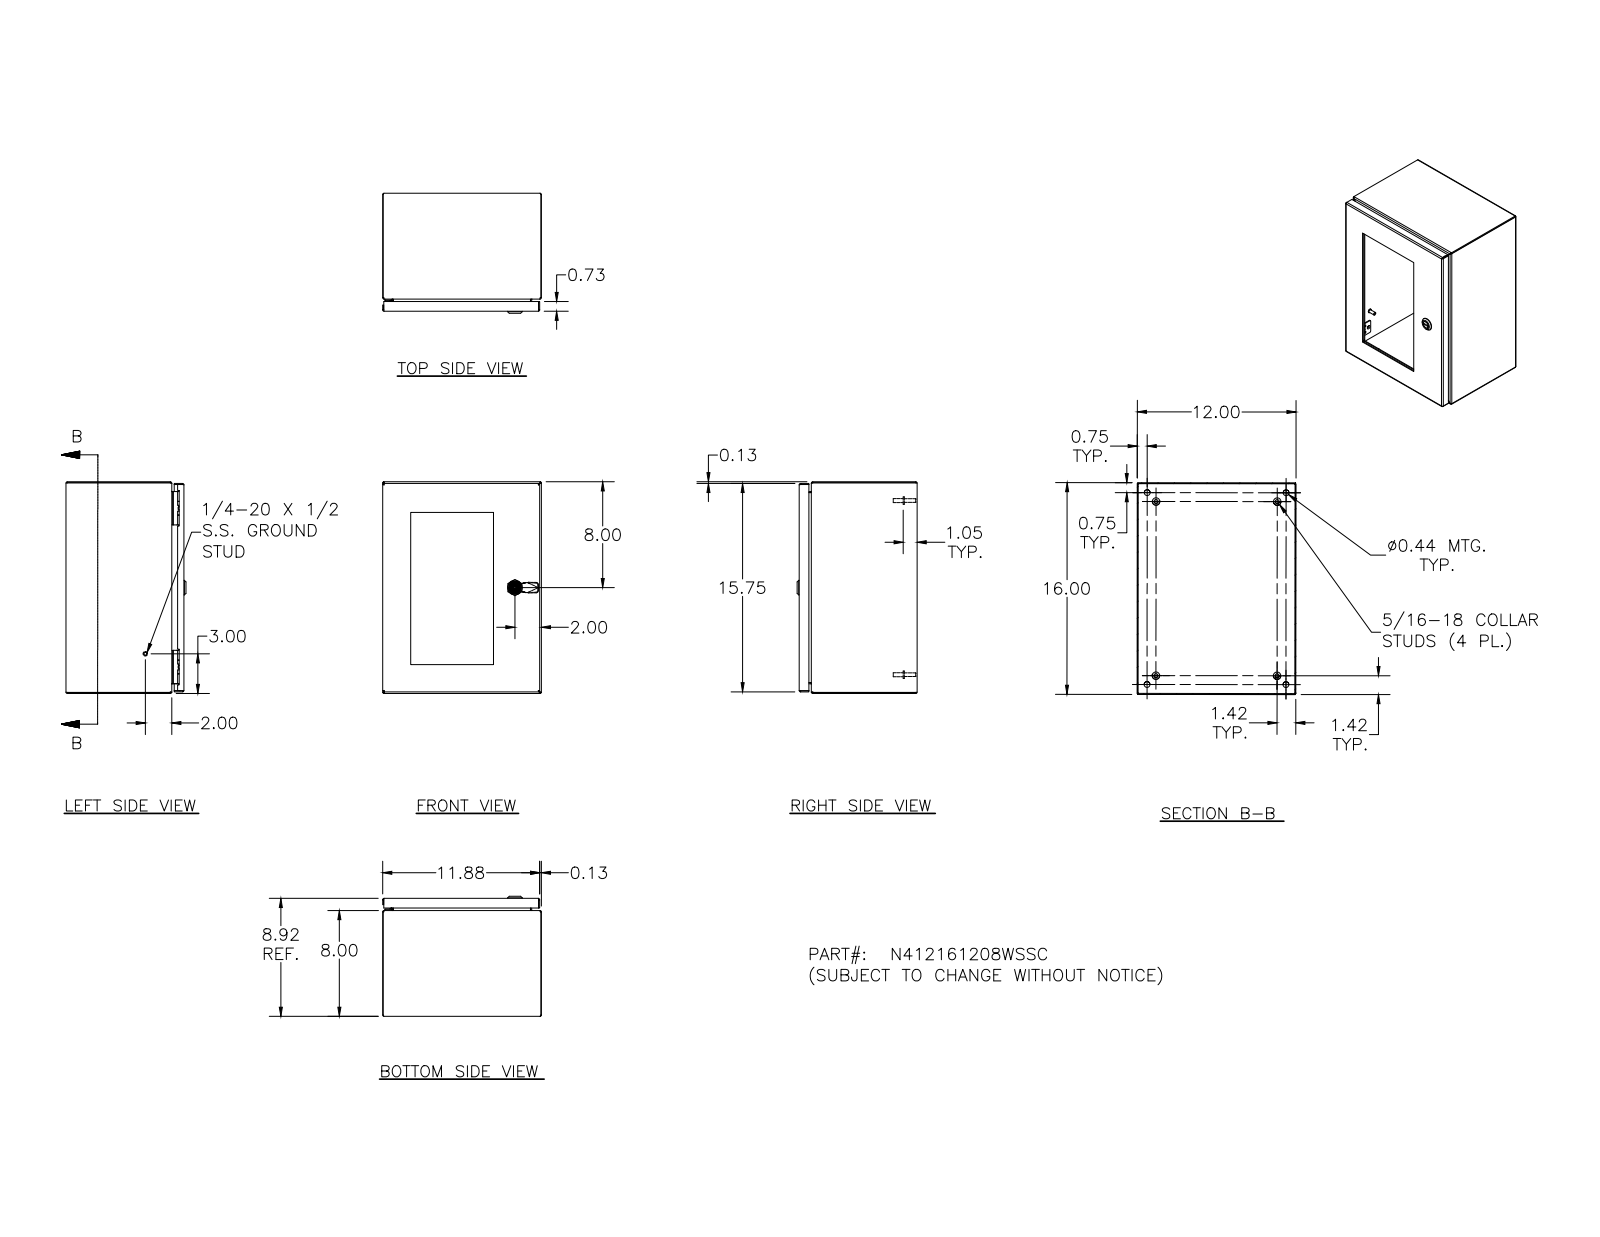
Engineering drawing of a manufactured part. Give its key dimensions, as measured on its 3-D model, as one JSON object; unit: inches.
{"part_name": "N412161208WSSC; N412161208WSSCBKP; N4121612WSSCLID; HFW328176 (+8 more)", "step_written_by": "Autodesk Inventor 2011 (AUTOMOTIVE_DESIGN)", "units": "inches", "bodies": {"solids": 58, "faces": 1748, "planar": 688, "cylindrical": 541, "other": 519}, "overall_size": [16, 12, 9.075], "volume_in3": 91.17, "surface_area_in2": 2069, "round_holes": [[0.156, 12], [0.281, 10], [0.093, 4], [0.152, 4], [0.167, 4], [0.172, 4], [0.188, 4], [0.437, 4], [0.187, 1], [0.197, 1], [0.315, 1], [0.394, 1]], "round_bosses_or_shafts": [[0.25, 10], [0.19, 10], [0.253, 9], [0.563, 4], [0.36, 4], [0.32, 4], [0.3, 4], [0.275, 4]], "partial_cylinders_radius": [[0.031, 34], [0.05, 26], [0.105, 24], [0.016, 18], [0.125, 16], [0.02, 9], [0.032, 8], [0.157, 4]], "face_to_face_distances": [0.074, 8.843, 11.926, 15.926, 8.769, 11.852, 12, 8.917, 16, 15.852], "hole_center_spacings": [4, 12, 6.221, 8.5, 8.585, 11.862, 7.5, 0.5]}
